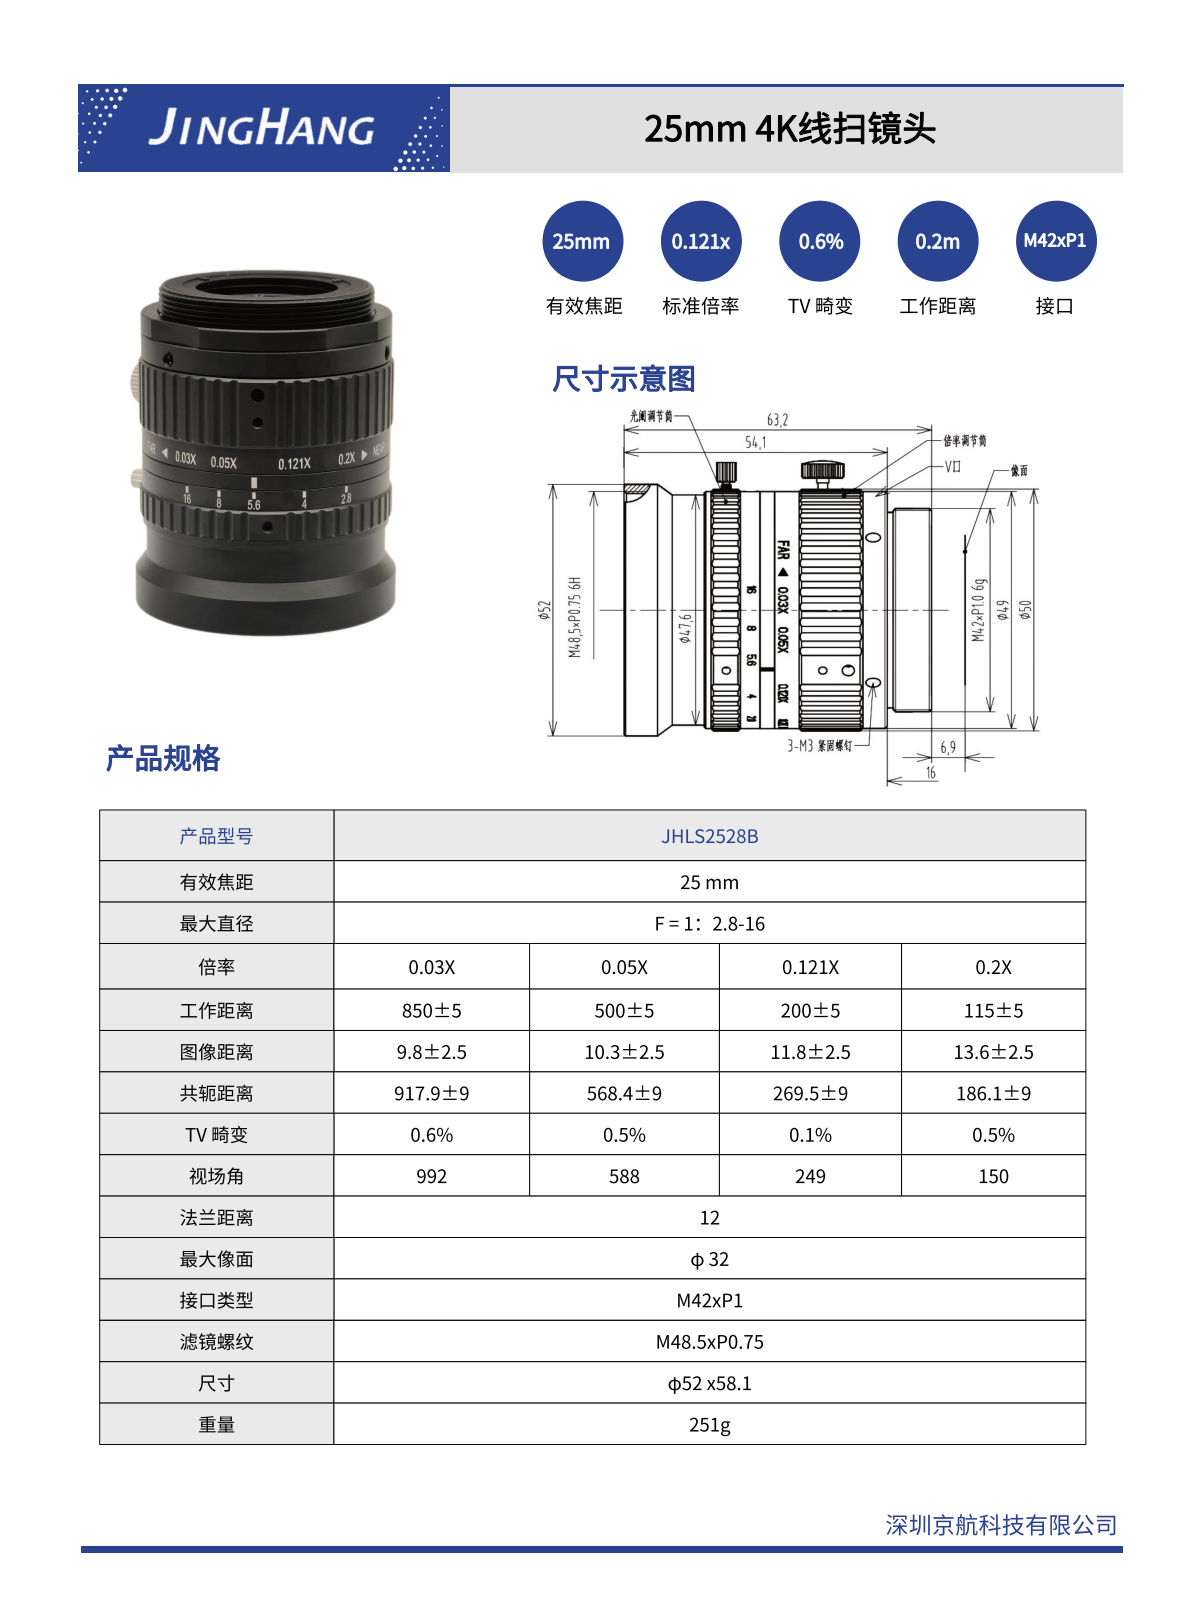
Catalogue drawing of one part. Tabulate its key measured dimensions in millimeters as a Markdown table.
| quantity | value |
| --- | --- |
| part name | 501_AF0; 305_AF0; 513_AF0; 601_AF0 (+8 more) |
| STEP written by | PRO/ENGINEER BY PARAMETRIC TECHNOLOGY CORPORATION, 2010020 (AUTOMOTIVE_DESIGN_CC2) |
| units | millimeters |
| bodies | 23 solids, 1780 faces (593 planar, 408 cylindrical, 779 other) |
| overall size | 65.51 × 57.05 × 53.89 |
| volume | 16 962 mm³ |
| surface area | 31 204 mm² |
| round holes (diameter × count) | 1.7 × 6, 2.5 × 6, 1.4 × 3, 1.5 × 3, 39.2 × 2, 0.6 × 1, 2.7 × 1, 22.6 × 1, 23.8 × 1, 25.26 × 1, 27.6 × 1, 32.6 × 1 |
| round bosses / shafts (diameter × count) | 2 × 8, 49 × 3, 1.4 × 3, 1.5 × 2, 53 × 1, 47.6 × 1, 42 × 1, 39 × 1 |
| partial cylindrical surfaces (radius × count) | 1.5 × 91, 24.49 × 2, 2 × 1, 25 × 1, 25.01 × 1 |
| main face-to-face distances | 56.32, 5.1, 51.22, 9, 42.22, 14.1, 6.9, 49.12, 58.12, 63.22 |
| hole center spacings | 15.06, 5.26, 15.05, 25.1, 5.25, 15.04, 19.85, 20.05 |
